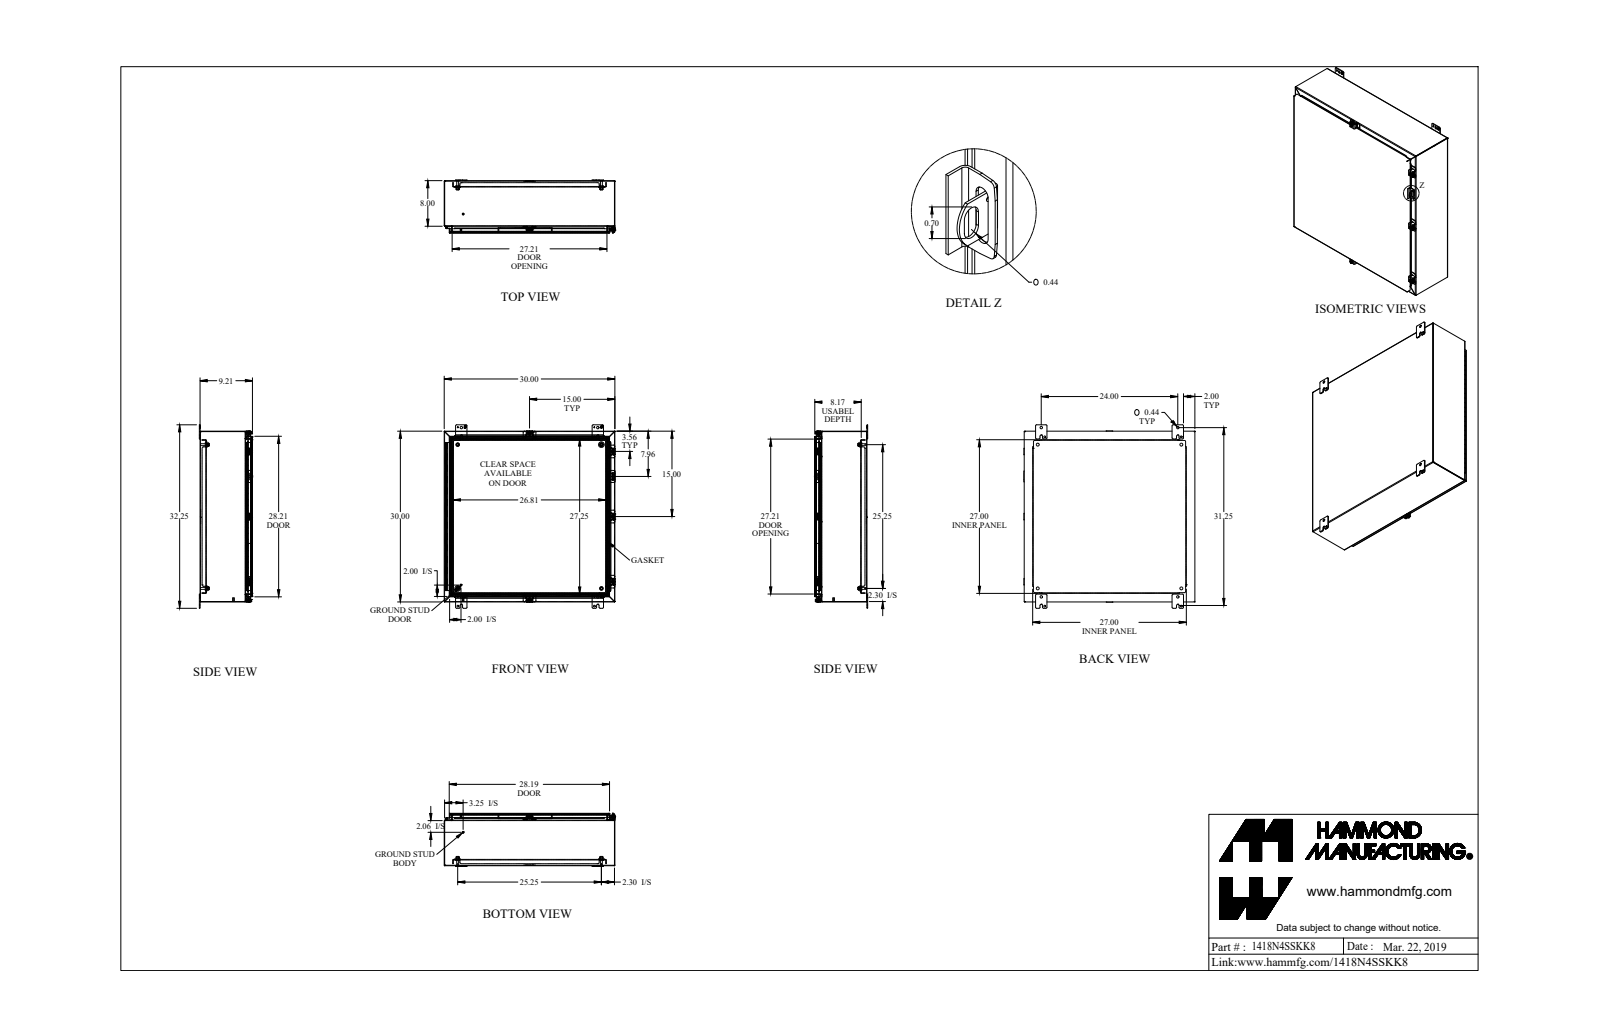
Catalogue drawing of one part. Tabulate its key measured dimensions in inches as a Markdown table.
| quantity | value |
| --- | --- |
| part name | 1418N4SSKK8_Default |
| STEP written by | SolidWorks 2019 (CONFIG_CONTROL_DESIGN) |
| units | inches |
| bodies | 43 solids, 1723 faces (1057 planar, 572 cylindrical, 94 other) |
| overall size | 32.25 × 30.063 × 9.375 |
| volume | 312.1 in³ |
| surface area | 8 148 in² |
| round holes (diameter × count) | 0.213 × 5, 0.265 × 5, 0.375 × 5, 0.313 × 4, 0.437 × 4, 0.5 × 4, 0.307 × 2, 0.445 × 2, 0.125 × 1, 0.187 × 1 |
| round bosses / shafts (diameter × count) | 0.5 × 5, 0.39 × 5, 0.244 × 5, 0.65 × 4, 0.375 × 4, 0.332 × 4, 1 × 2, 0.313 × 2 |
| partial cylindrical surfaces (radius × count) | 0.25 × 32, 0.048 × 27, 0.143 × 27, 0.188 × 26, 0.036 × 24, 0.108 × 24, 0.125 × 12, 0.141 × 10 |
| main face-to-face distances | 0.072, 29.928, 0.072, 9.066, 9.138, 9.138, 0.095, 9.21, 0.937, 1.009 |
| hole center spacings | 25.25, 30.146, 12.802, 1.736, 12.803, 24, 29.75, 35.709 |
